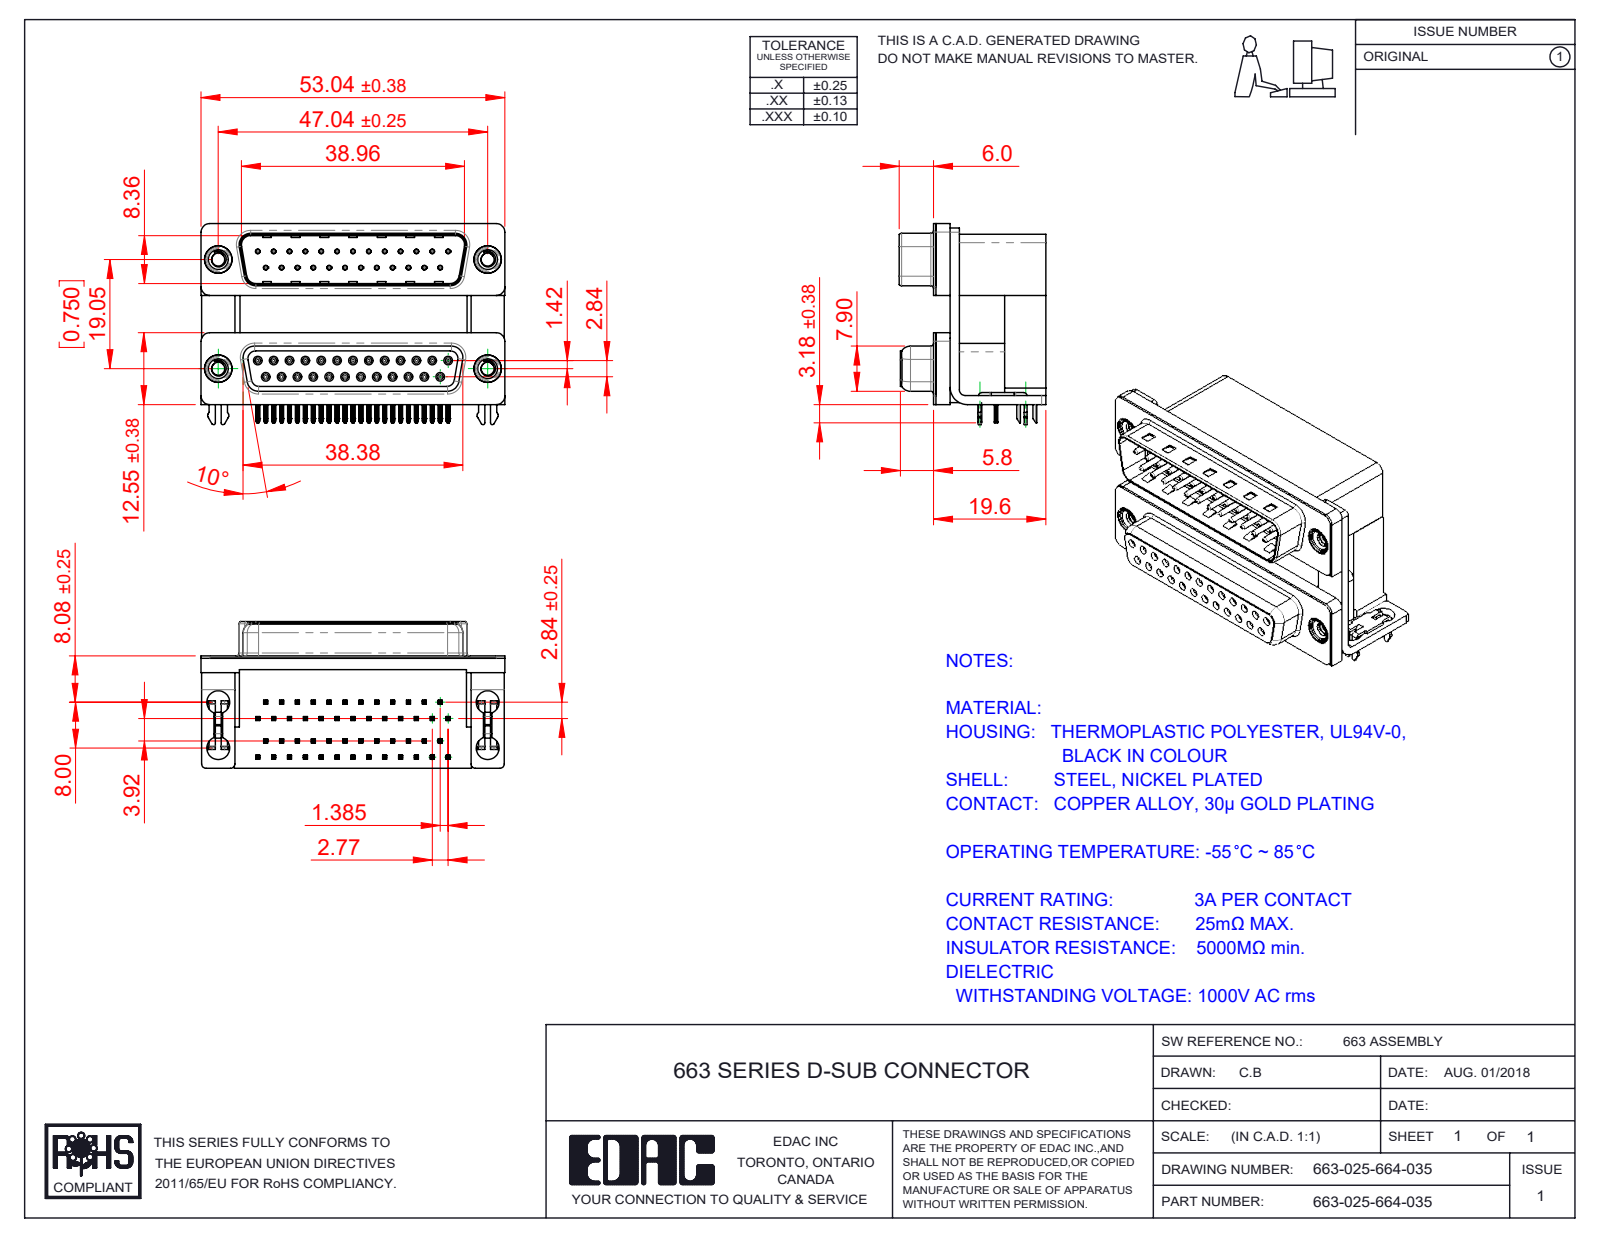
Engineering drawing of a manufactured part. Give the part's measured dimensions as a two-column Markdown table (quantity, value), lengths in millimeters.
| quantity | value |
| --- | --- |
| part name | 663 Contact Top Lower; 663 Contact Bottom Upper_M; 663 Housing Lower_25 Contacts; 663 Contact Top Upper_M (+8 more) |
| STEP written by | SolidWorks 2020 (CONFIG_CONTROL_DESIGN) |
| units | millimeters |
| bodies | 63 solids, 6355 faces (3359 planar, 1593 cylindrical, 1403 other) |
| overall size | 53.04 × 35.1 × 25.6 |
| volume | 22 585 mm³ |
| surface area | 24 141 mm² |
| round holes (diameter × count) | 0.8 × 50, 0.35 × 25, 0.9 × 25, 4 × 8, 2.26 × 4, 3.5 × 4, 4.8 × 4, 5 × 4 |
| round bosses / shafts (diameter × count) | 1.2 × 25, 0.75 × 25, 4.9 × 4, 4.75 × 4, 3.9 × 4 |
| partial cylindrical surfaces (radius × count) | 0.1 × 202, 0.25 × 110, 0.15 × 100, 0.12 × 50, 0.35 × 50, 0.34 × 25, 0.5 × 16, 1.5 × 14 |
| main face-to-face distances | 19.2, 0.4, 7.2, 12, 10.69, 16.7, 9.5, 2.5, 18.71, 29.4 |
| hole center spacings | 3.16, 2.77, 5.54, 11.08, 8.31, 5.03, 13.85, 7.48 |
